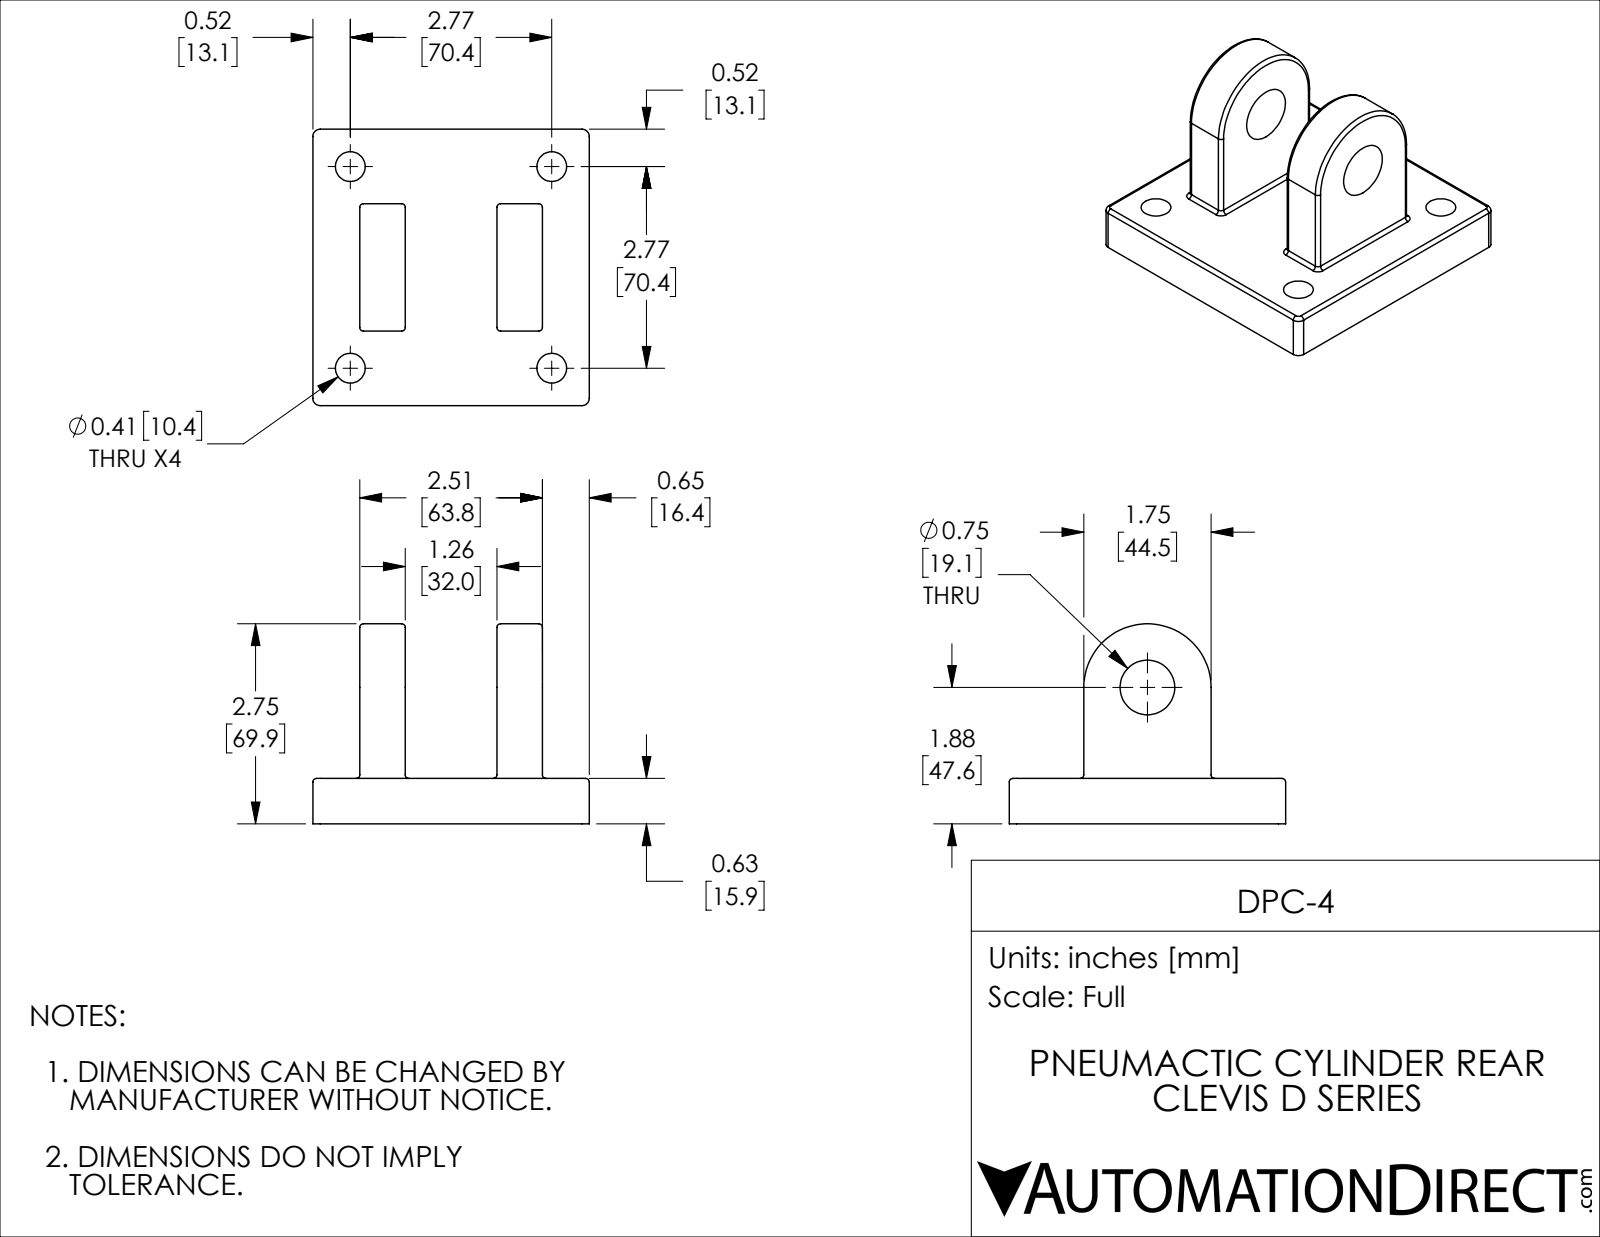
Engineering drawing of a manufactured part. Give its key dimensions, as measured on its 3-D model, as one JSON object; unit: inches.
{"part_name": "DPC-4", "step_written_by": "SolidWorks 2018 (AUTOMOTIVE_DESIGN)", "units": "inches", "bodies": {"solids": 1, "faces": 71, "planar": 14, "cylindrical": 39, "other": 18}, "overall_size": [3.8, 3.8, 2.75], "volume_in3": 12.36, "surface_area_in2": 58.56, "round_holes": [[0.41, 4], [0.752, 1]], "partial_cylinders_radius": [[0.05, 18], [0.1, 4], [0.875, 1]], "face_to_face_distances": [0.625, 1.885, 0.645, 1.27, 2.53, 3.155, 3.8, 2.51, 1.26, 1.025], "hole_center_spacings": [2.77, 3.917]}
